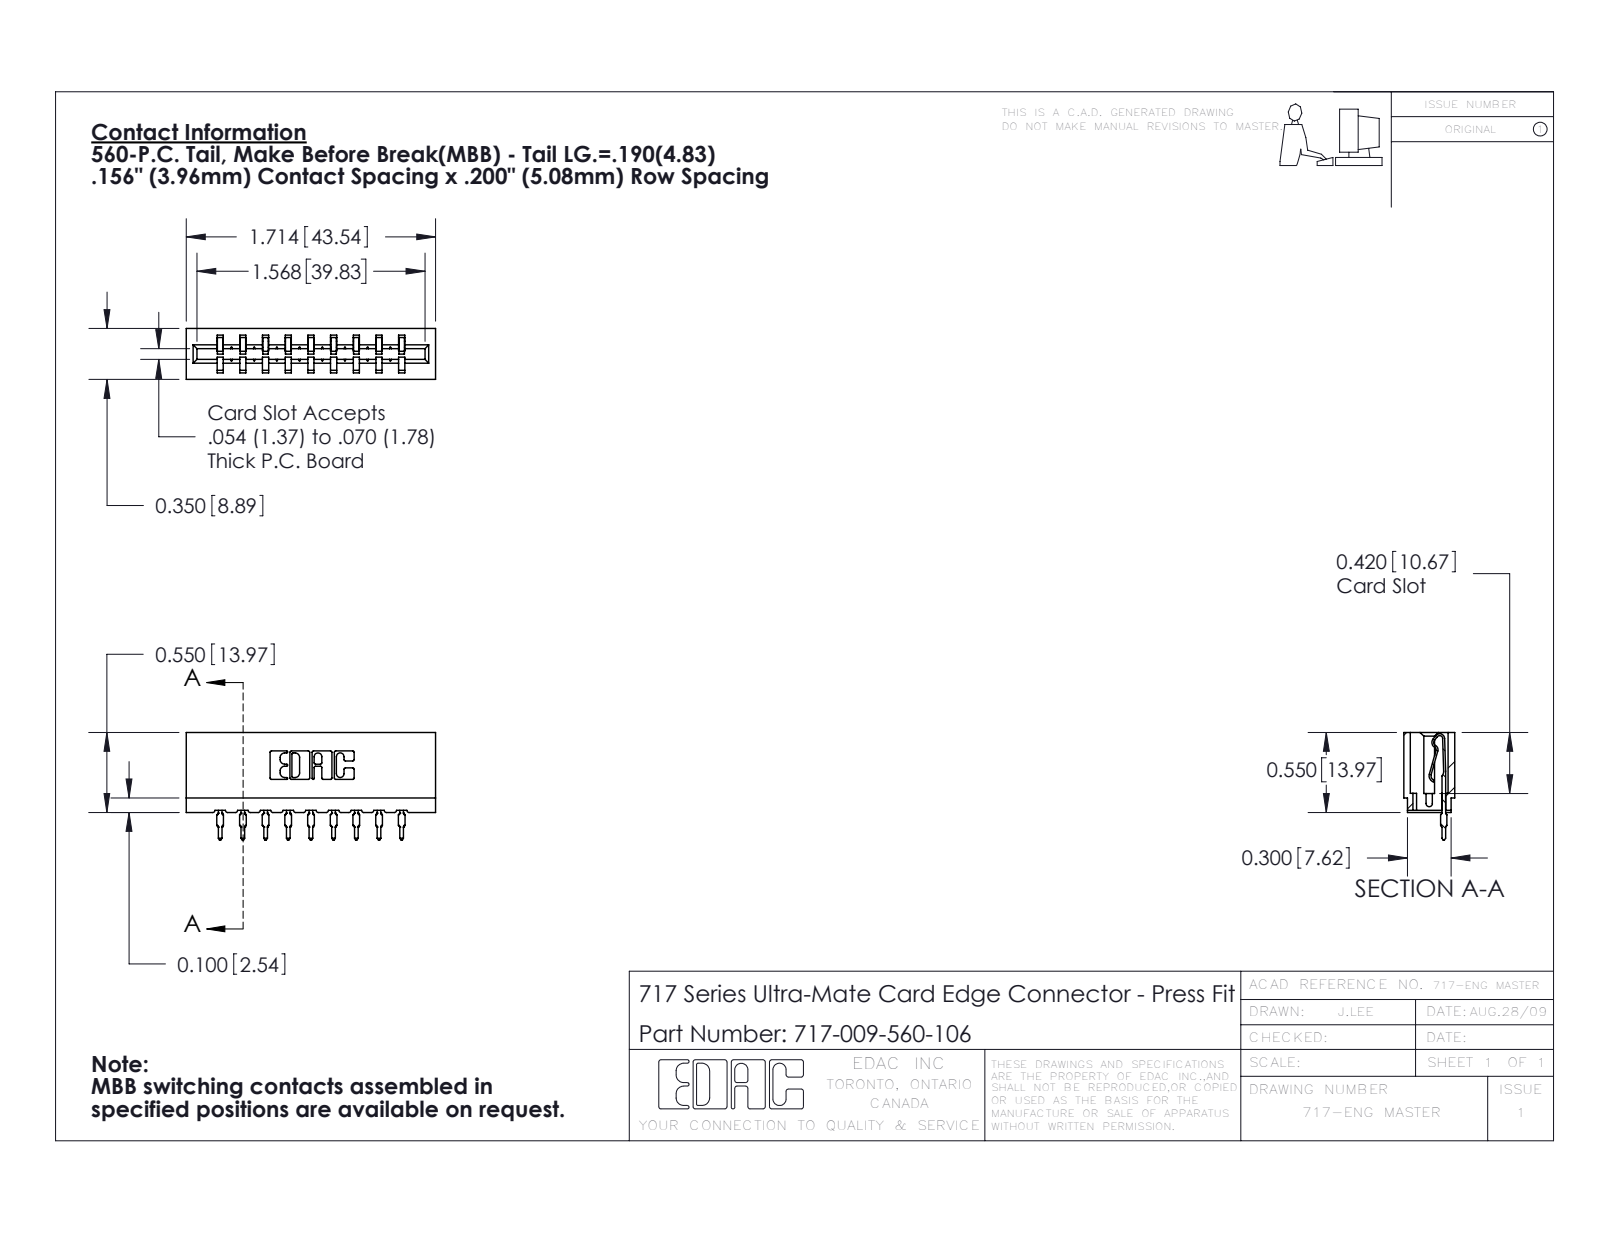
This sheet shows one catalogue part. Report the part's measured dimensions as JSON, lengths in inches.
{"part_name": "745-292-001_560; 717-009-560-106; 717 Part_Insulator Option - 06", "step_written_by": "SolidWorks 2016 (CONFIG_CONTROL_DESIGN)", "units": "inches", "bodies": {"solids": 10, "faces": 1192, "planar": 711, "cylindrical": 247, "other": 234}, "overall_size": [1.714, 0.739, 0.35], "volume_in3": 0.235, "surface_area_in2": 8.061, "partial_cylinders_radius": [[0.01, 22], [0.015, 18], [0.021, 18], [0.007, 6], [0.031, 6], [0.005, 4], [0.011, 4], [0.026, 3]], "face_to_face_distances": [0.156, 0.212, 0.624, 0.138, 0.468, 0.198, 0.35, 0.312, 0.042, 0.312]}
